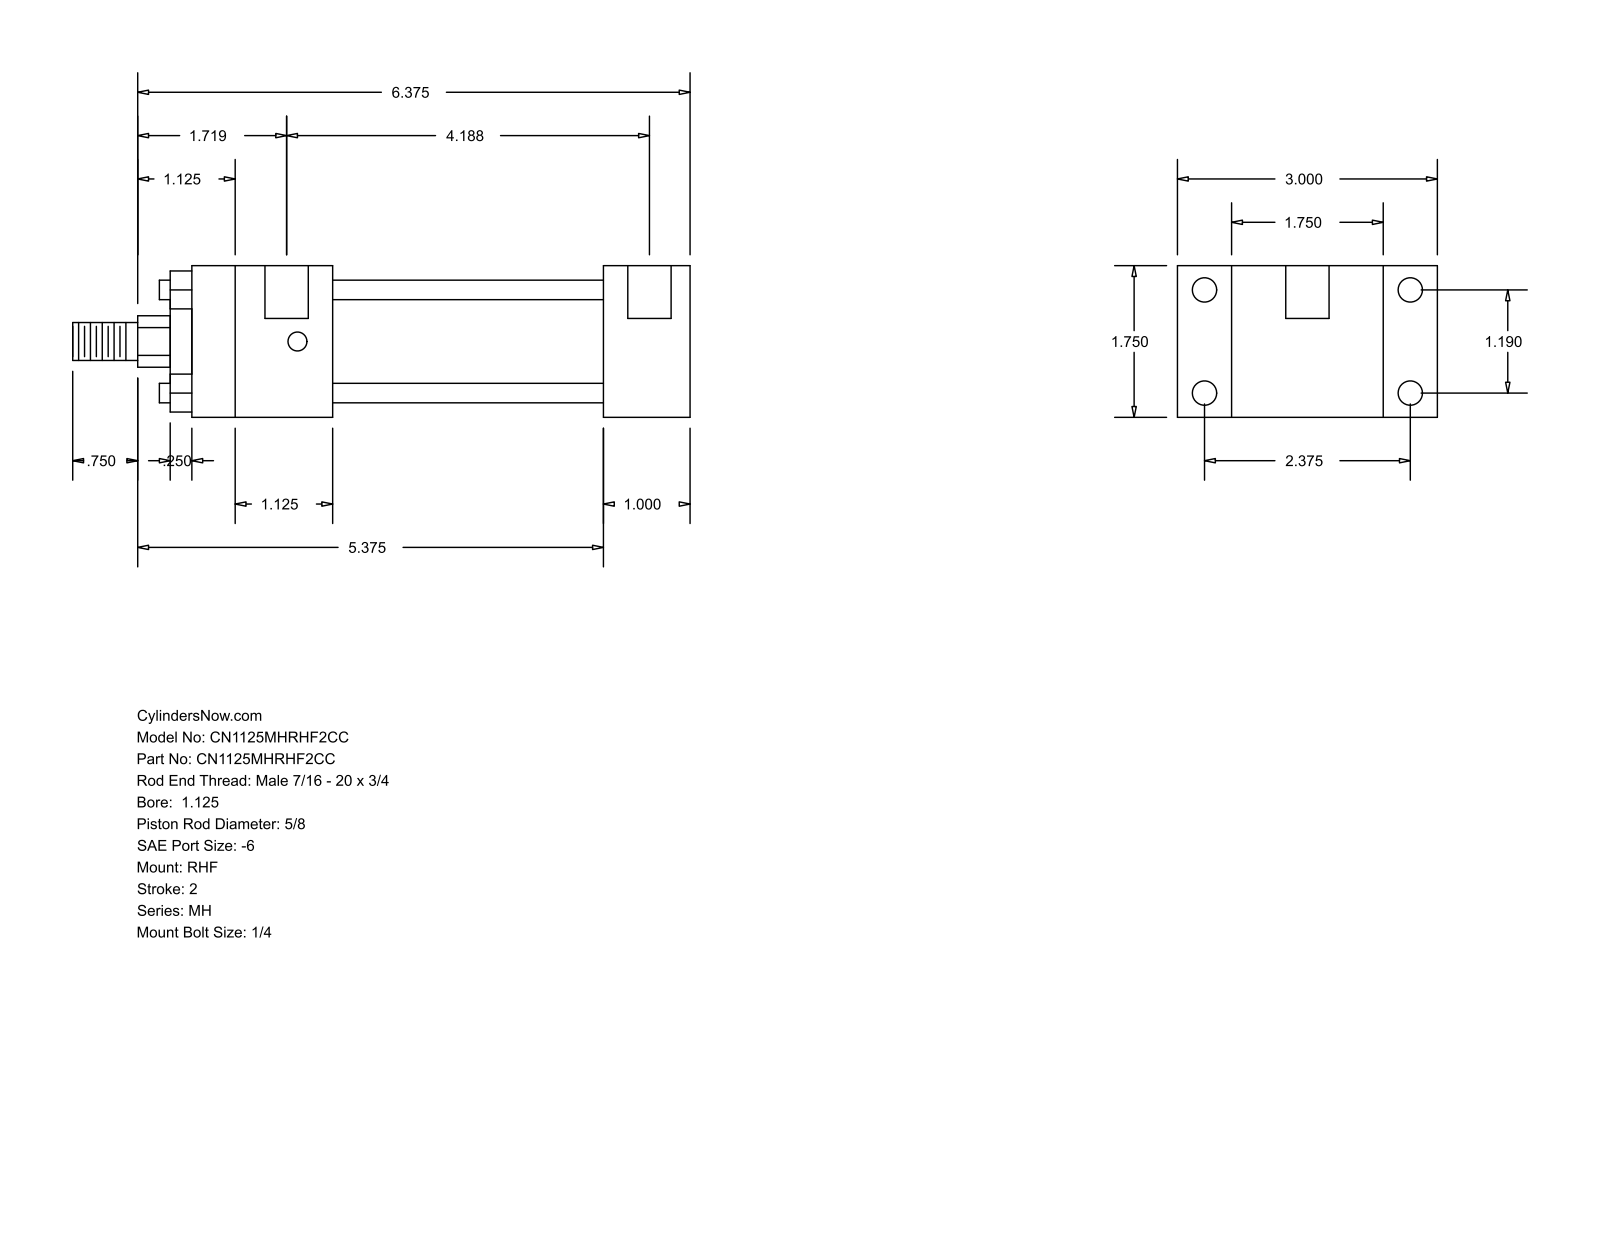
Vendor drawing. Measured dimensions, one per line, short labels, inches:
name: MH_RHF__0112_0.625
written by: GSSL Pune (CONFIG_CONTROL_DESIGN)
unit: in
bodies: 0 solids, 88 faces (60 planar, 28 cylindrical, 0 other)
size: 7.125 × 3 × 1.75
holes: 4× ⌀0.219, 4× ⌀0.281, 2× ⌀0.5
bosses: 4× ⌀0.225, 1× ⌀1.375, 1× ⌀1.125, 1× ⌀0.625, 1× ⌀0.437
rounds: 1× R0.297
face distances: 1.75, 0.625, 1, 2.375, 3, 3.125, 4.125, 1.625, 4.75, 5.75
hole spacings: 1.19, 2.375, 2.656, 4.063, 0.125, 4.187
